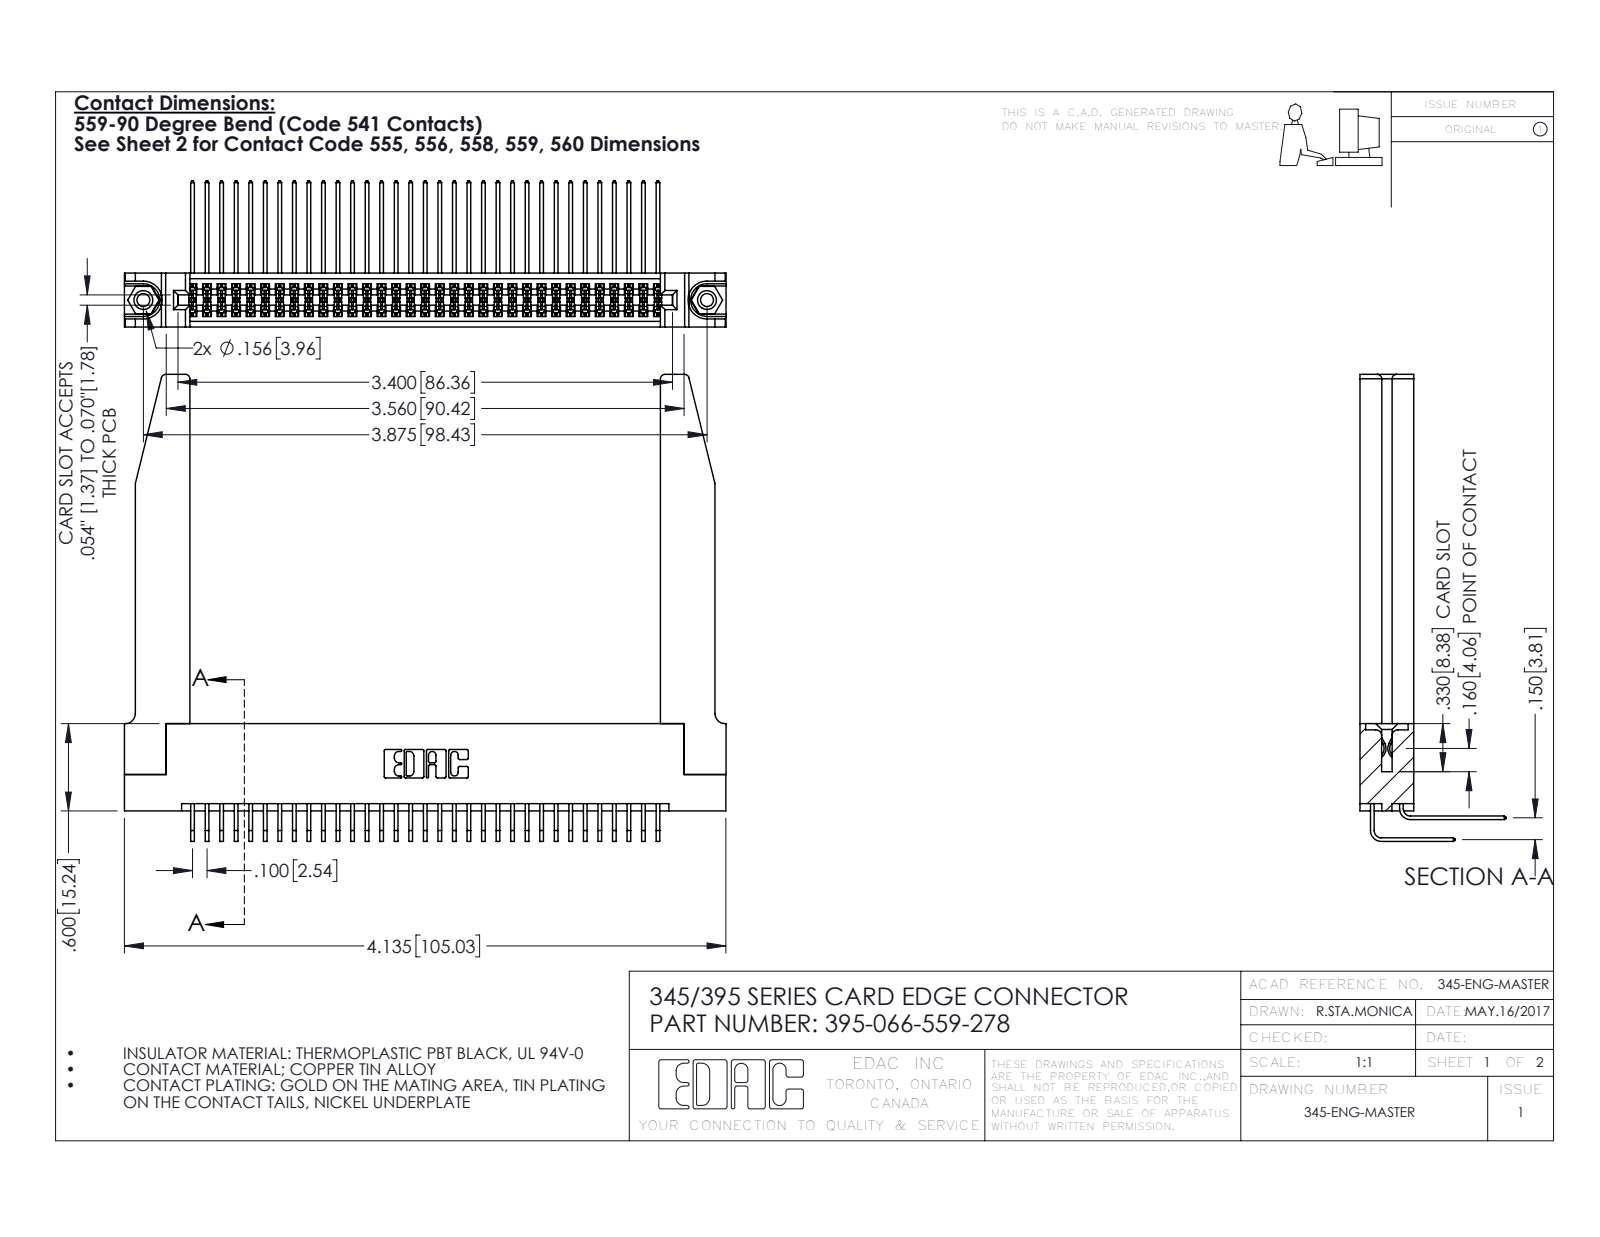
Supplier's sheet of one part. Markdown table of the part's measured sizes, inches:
| quantity | value |
| --- | --- |
| part name | 395-066-559-278; 345-292-001_558 559 Tail - 1; 345-292-001_559 Tail - 2; 345 Part_Flush Mounting Lugs - 0.156 Dia-TH (+2 more) |
| STEP written by | SolidWorks 2016 (CONFIG_CONTROL_DESIGN) |
| units | inches |
| bodies | 71 solids, 3792 faces (2532 planar, 1208 cylindrical, 52 other) |
| overall size | 4.136 × 3.209 × 1.005 |
| volume | 1.115 in³ |
| surface area | 37.17 in² |
| round holes (diameter × count) | 0.089 × 2, 0.125 × 2, 0.156 × 2, 0.064 × 1 |
| round bosses / shafts (diameter × count) | 0.155 × 2 |
| partial cylindrical surfaces (radius × count) | 0.006 × 99, 0.01 × 22, 0.03 × 8, 0.007 × 6, 0.031 × 6, 0.026 × 3, 0.014 × 2, 0.019 × 2 |
| main face-to-face distances | 0.37, 0.072, 0.298, 0.2, 0.098, 0.272, 0.025, 0.225, 0.175, 0.15 |
| hole center spacings | 0.27, 3.64, 3.875 |
